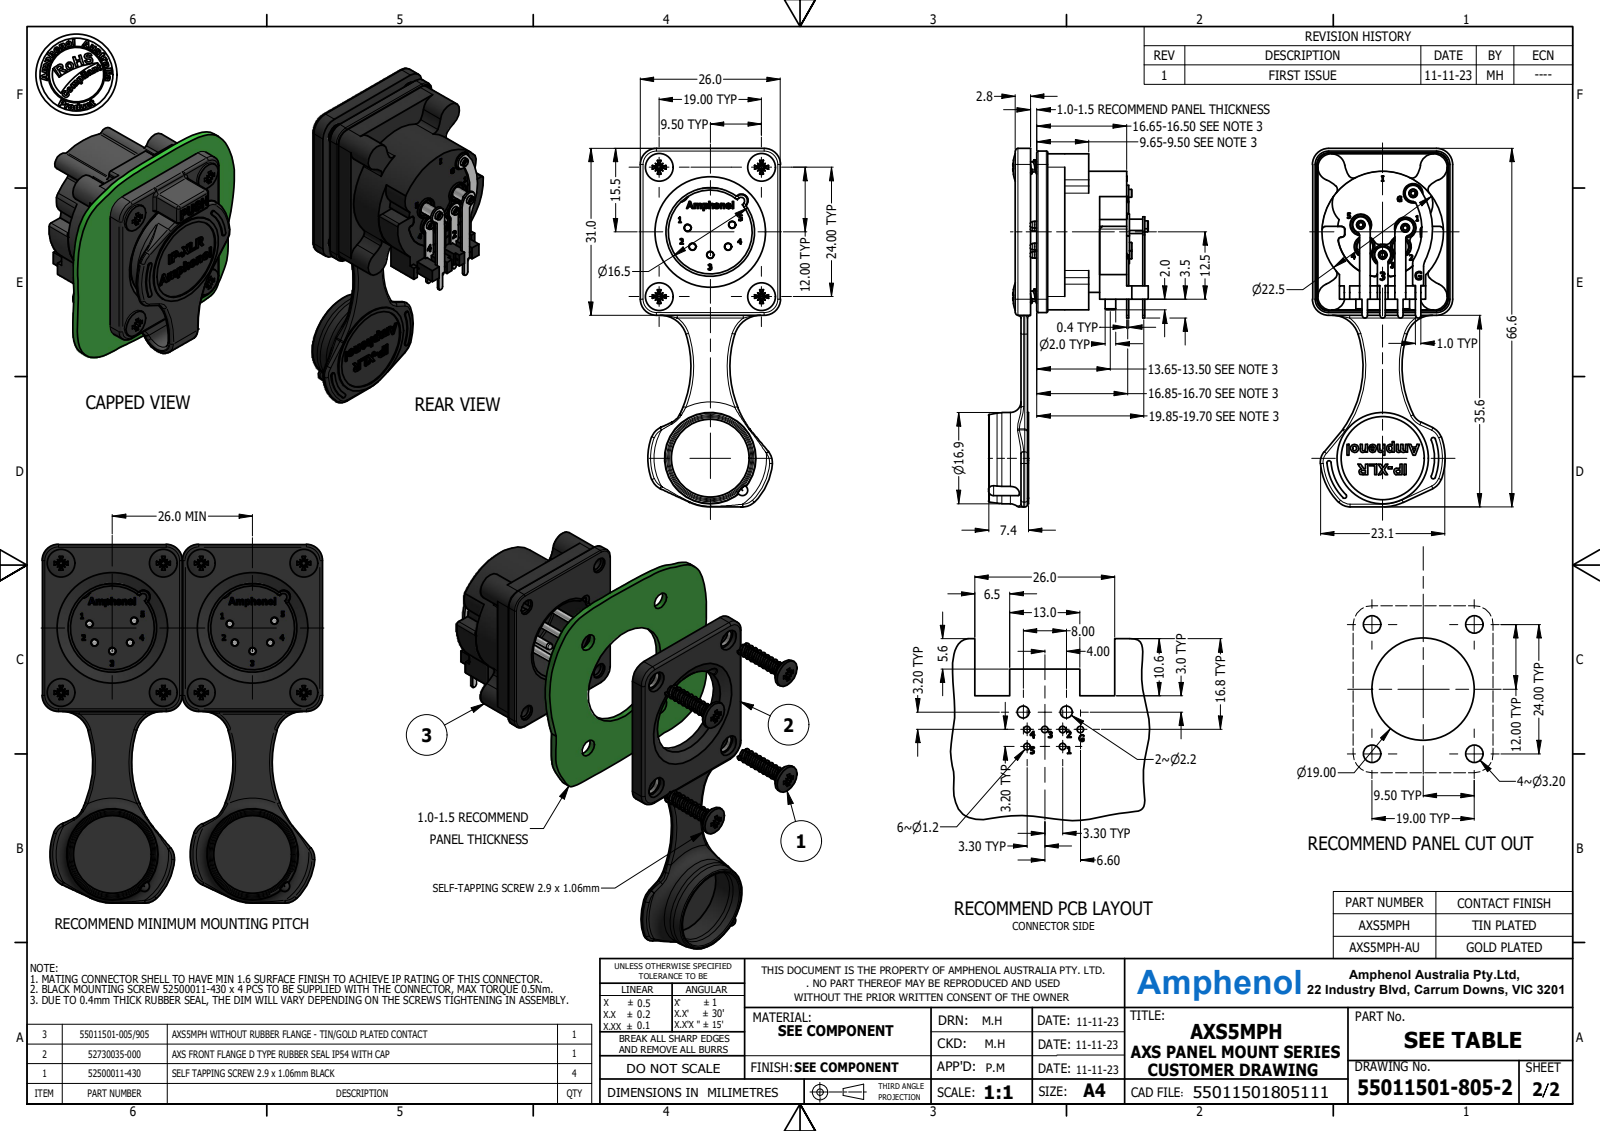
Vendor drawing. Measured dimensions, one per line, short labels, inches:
name: 55011501-805
written by: Autodesk Inventor 2023 (AUTOMOTIVE_DESIGN)
unit: in
bodies: 1 solid, 2476 faces (729 planar, 529 cylindrical, 1218 other)
size: 2.62 × 1.165 × 1.024
volume: 0.562 in³; area: 14.29 in²
holes: 6× ⌀0.031, 6× ⌀0.063, 5× ⌀0.052, 5× ⌀0.085, 4× ⌀0.094, 4× ⌀0.134, 4× ⌀0.157, 2× ⌀0.126, 1× ⌀0.102, 1× ⌀0.142, 1× ⌀0.567, 1× ⌀0.606
bosses: 6× ⌀0.059, 5× ⌀0.083, 5× ⌀0.05, 2× ⌀0.079, 1× ⌀0.886, 1× ⌀0.669, 1× ⌀0.665, 1× ⌀0.157
rounds: 45× R0.02, 16× R0.039, 12× R0.016, 12× R0.045, 12× R0.118, 11× R0.079, 10× R0.197, 9× R0.059
face distances: 0.022, 0.063, 0.085, 0.089, 0.173, 0.11, 0.02, 0.132, 0.069, 0.047
hole spacings: 0.603, 0.169, 0.143, 0.168, 0.439, 0.482, 0.622, 0.63
